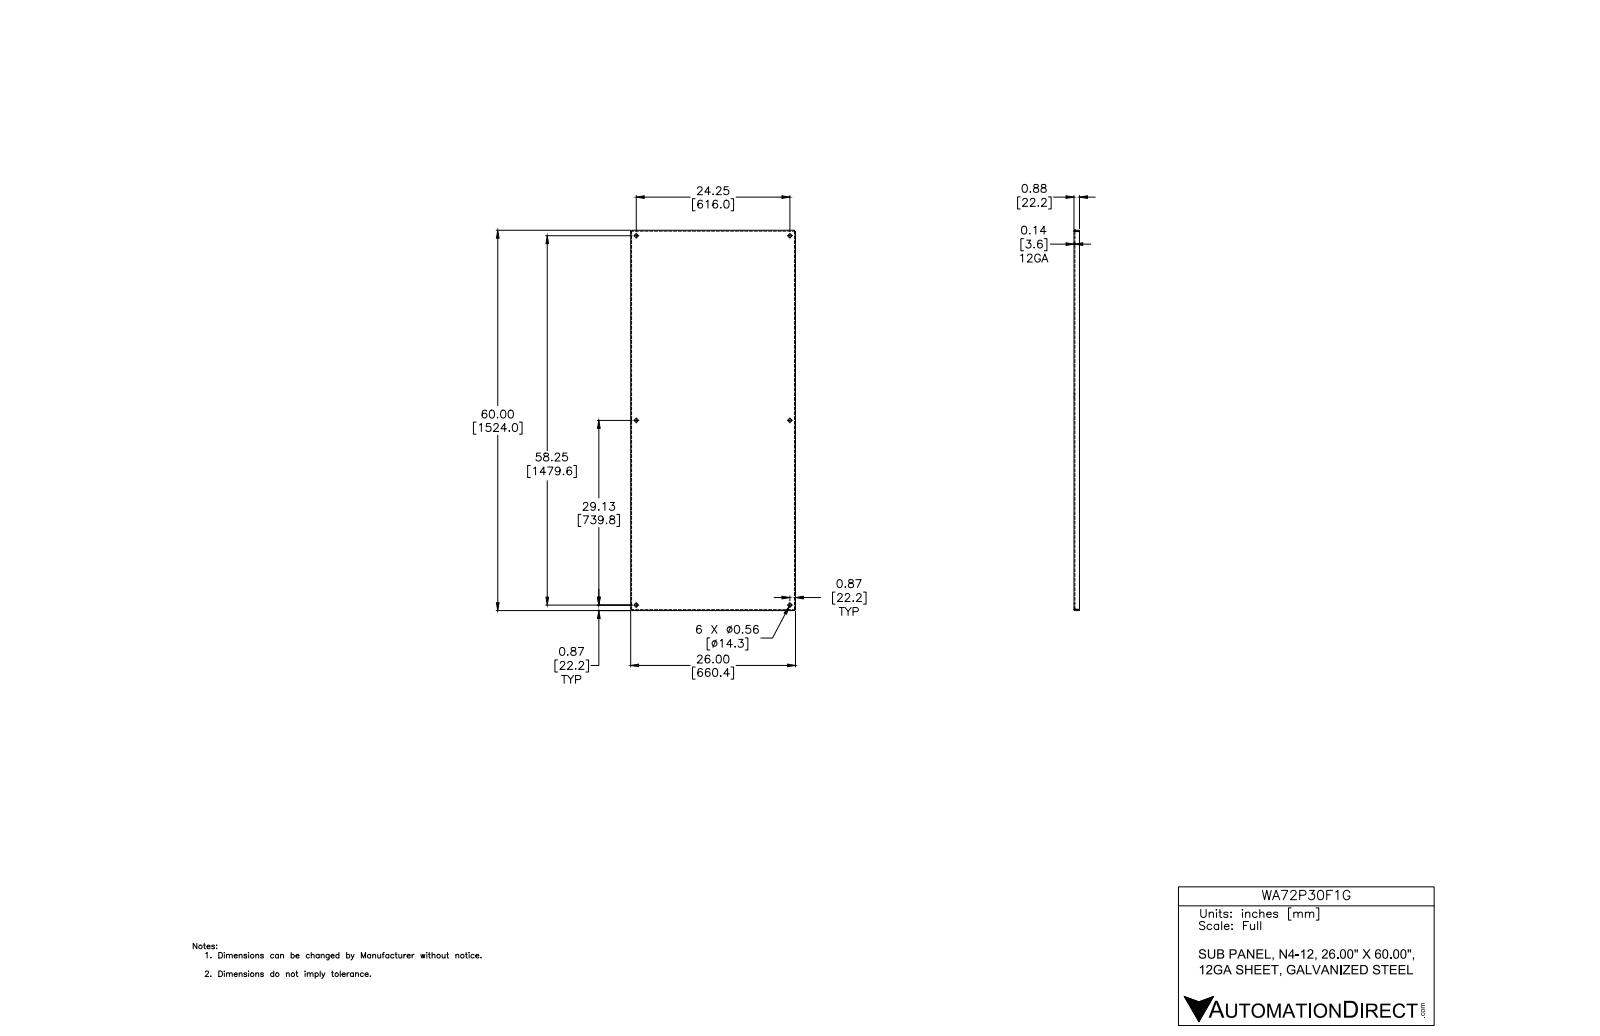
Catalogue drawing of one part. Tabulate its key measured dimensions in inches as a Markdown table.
| quantity | value |
| --- | --- |
| part name | WA_P_F_G |
| STEP written by | Autodesk Inventor 2012 (AUTOMOTIVE_DESIGN) |
| units | inches |
| bodies | 1 solid, 44 faces (22 planar, 14 cylindrical, 8 other) |
| overall size | 60 × 26 × 0.875 |
| volume | 158.2 in³ |
| surface area | 3 392 in² |
| round holes (diameter × count) | 0.563 × 6 |
| partial cylindrical surfaces (radius × count) | 0.016 × 4, 0.109 × 4 |
| main face-to-face distances | 0.094, 25.906, 26, 25.813, 59.906, 60, 59.813, 0.781, 0.875, 0.16 |
| hole center spacings | 37.899, 24.25, 29.125, 29.125, 58.25, 63.096, 24.25, 37.899 |
